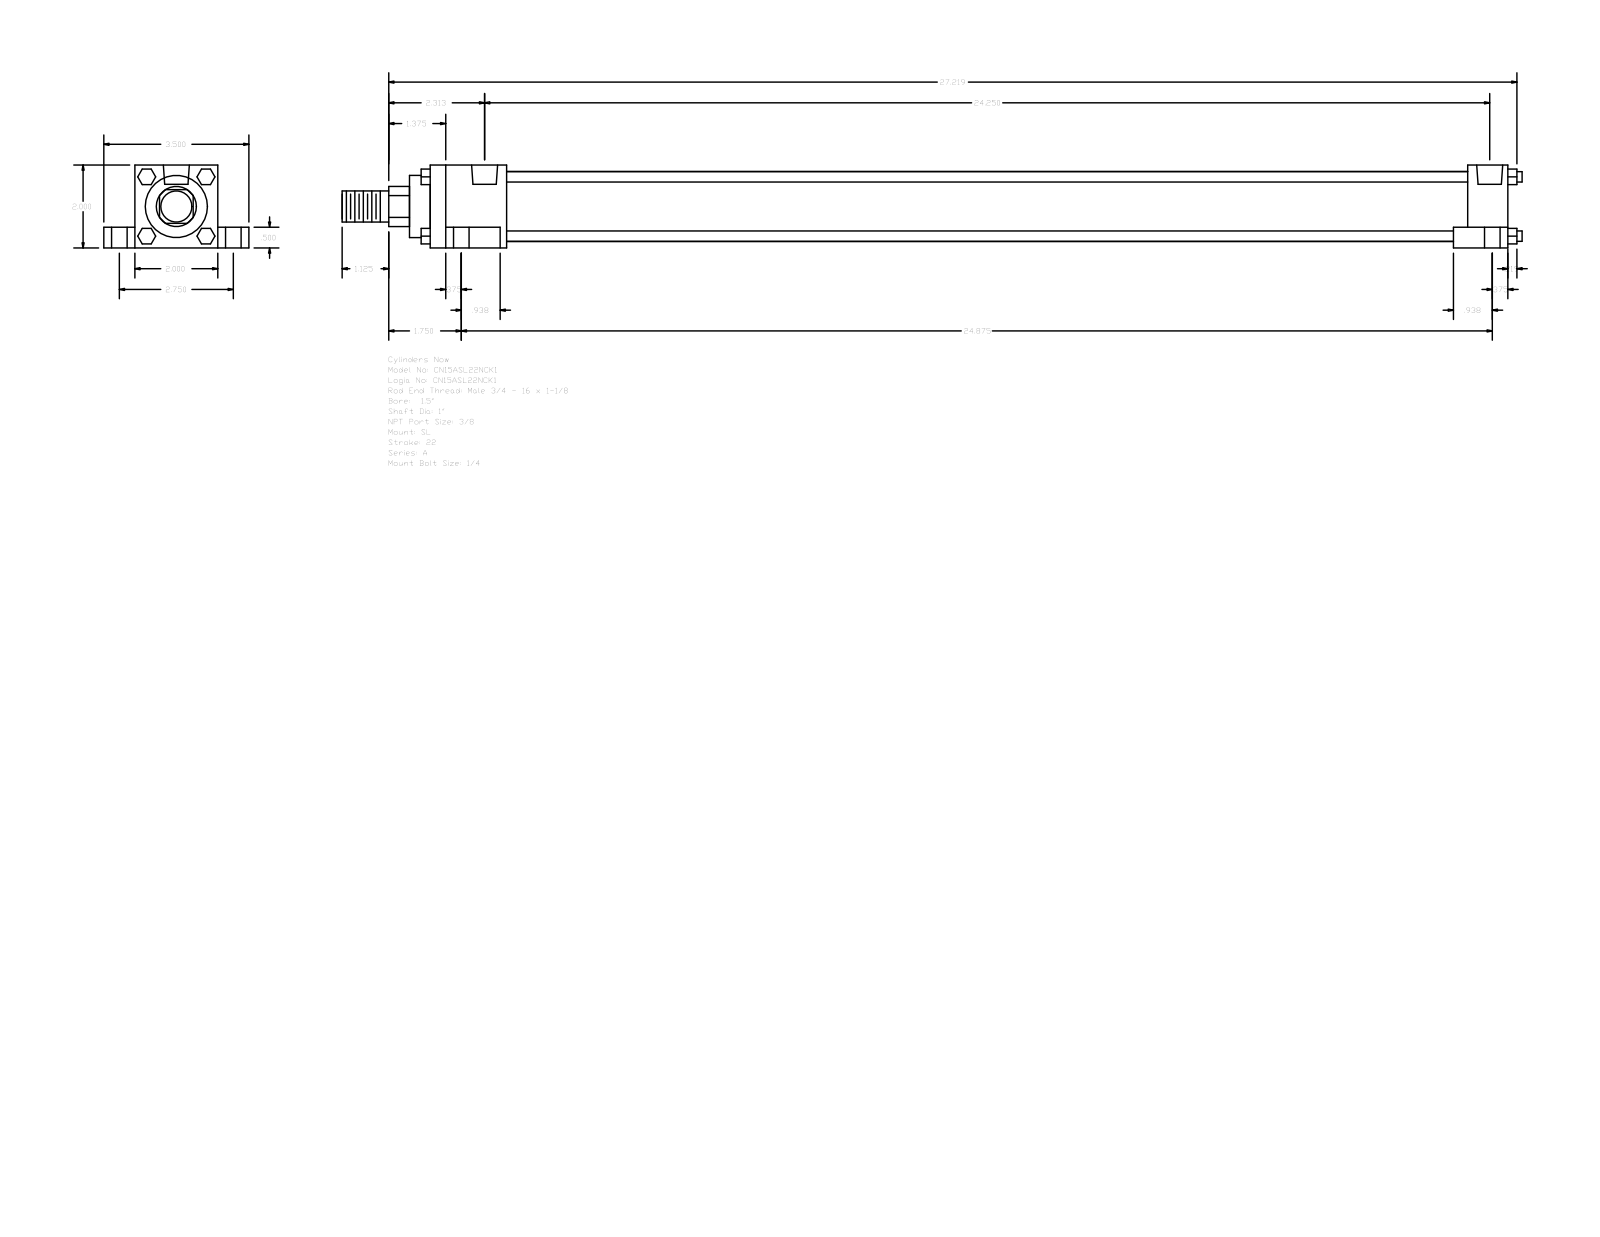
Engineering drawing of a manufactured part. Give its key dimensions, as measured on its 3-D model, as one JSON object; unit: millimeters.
{"part_name": "A_SL__0150_1", "step_written_by": "GSSL Pune (CONFIG_CONTROL_DESIGN)", "units": "millimeters", "bodies": {"solids": 0, "faces": 148, "planar": 112, "cylindrical": 36, "other": 0}, "overall_size": [723.11, 88.9, 50.8], "round_holes": [[5.56, 4], [9.53, 4], [15.88, 4], [15.93, 2]], "round_bosses_or_shafts": [[6.35, 4], [42.93, 1], [38.1, 1], [25.4, 1], [19.05, 1]], "partial_cylinders_radius": [[12.29, 1]], "face_to_face_distances": [50.8, 12.7, 38.1, 19.05, 69.85, 9.52, 660.4, 33.34, 635.79, 24.61], "hole_center_spacings": [3.97, 34.96, 35.36, 37.73, 39.41, 69.84, 608.01, 611.98]}
